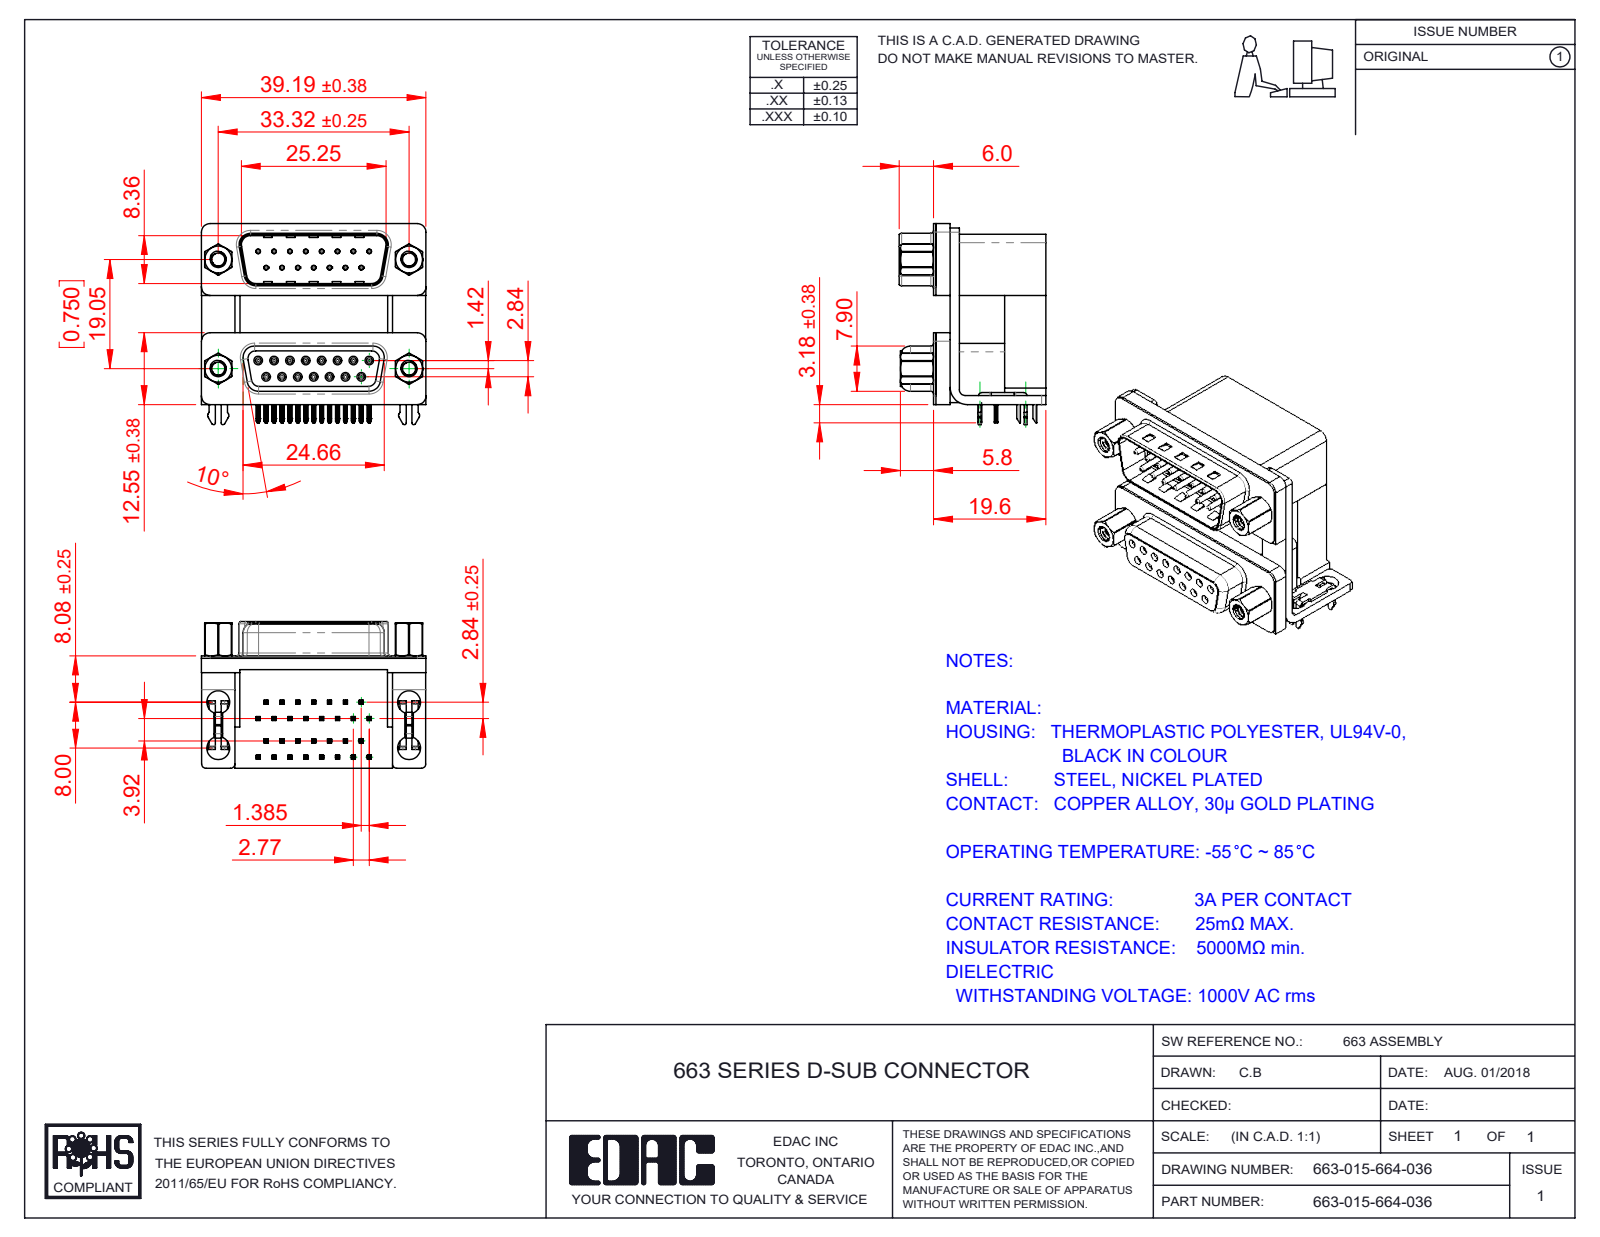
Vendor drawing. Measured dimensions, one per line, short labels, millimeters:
name: 663 Housing Spacer_15 Contacts M; 663 Mounting Bracket_2ProngM; 663 Contact Top Upper_M; 663 Shell Plug_15 Contacts (+8 more)
written by: SolidWorks 2020 (CONFIG_CONTROL_DESIGN)
unit: mm
bodies: 47 solids, 4316 faces (2161 planar, 1208 cylindrical, 947 other)
size: 39.19 × 35.1 × 25.6
volume: 15 665 mm³; area: 17 959 mm²
holes: 30× ⌀0.8, 15× ⌀0.35, 15× ⌀0.9, 8× ⌀4, 4× ⌀2.26, 4× ⌀2.29, 4× ⌀3.5, 4× ⌀4.8, 4× ⌀5
bosses: 15× ⌀1.2, 15× ⌀0.75, 4× ⌀4.9, 4× ⌀4.75, 4× ⌀3.9, 4× ⌀2.79
rounds: 122× R0.1, 70× R0.25, 60× R0.15, 30× R0.12, 30× R0.35, 16× R0.5, 16× R1.5, 15× R0.34
face distances: 0.4, 19.2, 16.7, 2.5, 7.2, 12, 9.5, 19.6, 12.4, 2.9
hole spacings: 3.16, 19.25, 2.77, 19.84, 5.54, 8.31, 19.05, 20.78
